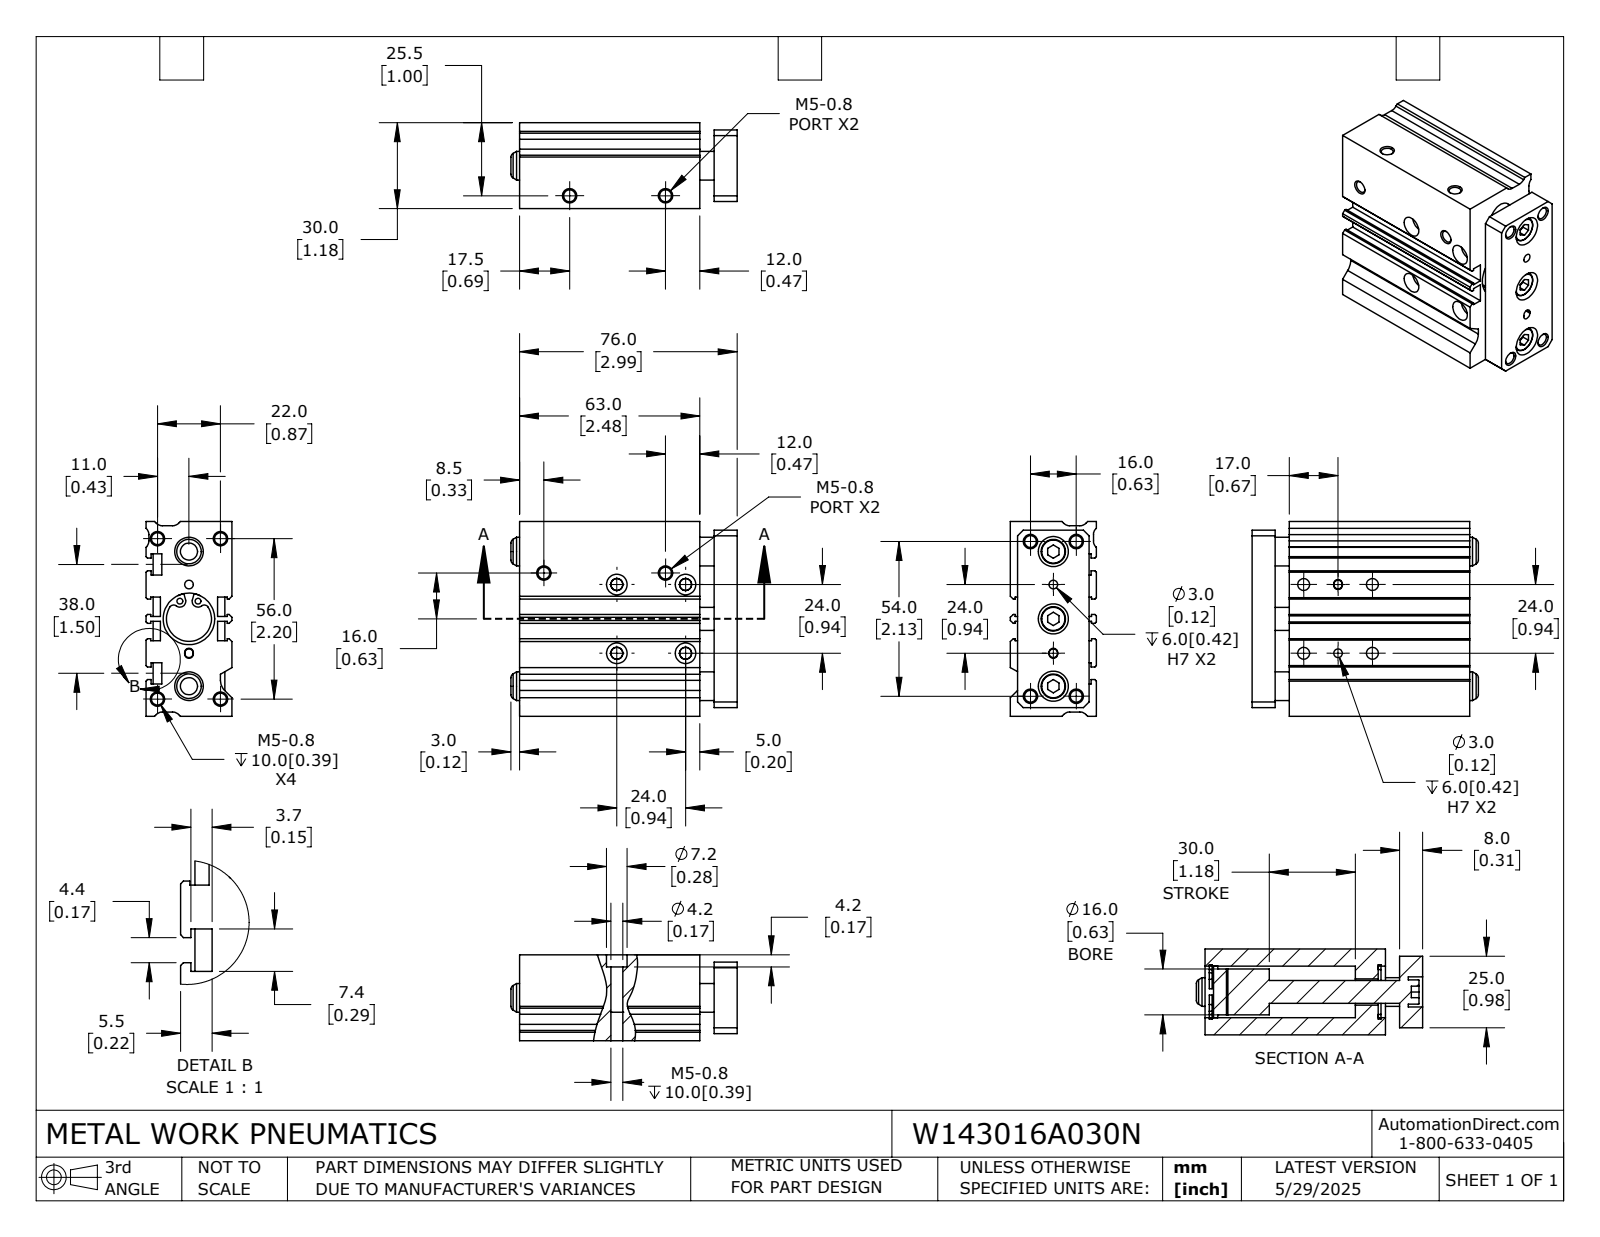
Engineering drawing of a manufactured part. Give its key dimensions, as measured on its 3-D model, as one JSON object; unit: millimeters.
{"part_name": "W143016A030_BODY; W143016A030_ROD; W143016A030N", "step_written_by": "SolidWorks 2024 (CONFIG_CONTROL_DESIGN)", "units": "millimeters", "bodies": {"solids": 5, "faces": 344, "planar": 169, "cylindrical": 137, "other": 38}, "overall_size": [79, 68, 30], "volume_mm3": 113518, "surface_area_mm2": 44715, "round_holes": [[4.13, 16], [2, 4], [3, 4], [4.2, 4], [7.2, 4], [10.5, 3], [10, 2], [9.2, 1], [15.7, 1], [18, 1]], "round_bosses_or_shafts": [[8.5, 3], [19, 2], [16, 1], [8, 1]], "partial_cylinders_radius": [[3, 6], [1.5, 4], [1.58, 4], [2.07, 4], [5, 1]], "face_to_face_distances": [5, 68, 30, 2.5, 25, 8, 1.5, 63, 3, 13], "hole_center_spacings": [12, 24, 3.16, 6.62, 6.95, 8.73, 11.88, 17]}
